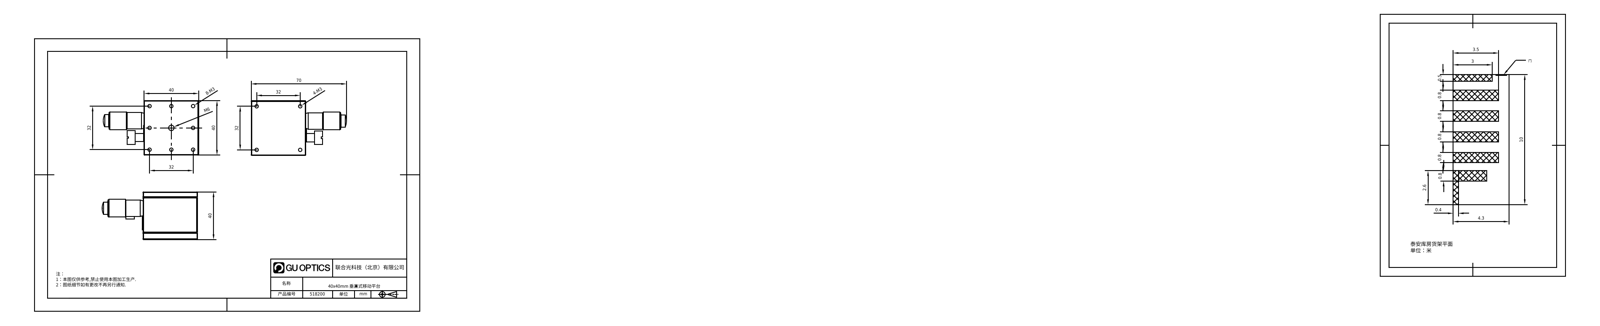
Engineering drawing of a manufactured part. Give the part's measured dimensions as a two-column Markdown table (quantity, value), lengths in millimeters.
| quantity | value |
| --- | --- |
| part name | 518200 |
| STEP written by | SolidWorks 2020 (CONFIG_CONTROL_DESIGN) |
| units | millimeters |
| bodies | 0 solids, 298 faces (185 planar, 92 cylindrical, 21 other) |
| overall size | 70 × 40 × 35 |
| round holes (diameter × count) | 2.5 × 16, 1.6 × 6, 3 × 6, 5 × 6, 2.12 × 5, 3.5 × 4, 2.2 × 2, 4 × 2, 6 × 2, 9.5 × 1, 10.5 × 1 |
| round bosses / shafts (diameter × count) | 13 × 1, 12 × 1, 10 × 1, 9 × 1, 6 × 1, 5 × 1 |
| partial cylindrical surfaces (radius × count) | 1.67 × 8, 1 × 5, 3 × 4, 1.75 × 2, 2 × 1 |
| main face-to-face distances | 5, 4, 30, 26, 31, 35, 11, 6, 0.5, 40 |
| hole center spacings | 16, 22.63, 35.78, 32, 7.16, 15, 17.76, 18.43 |
